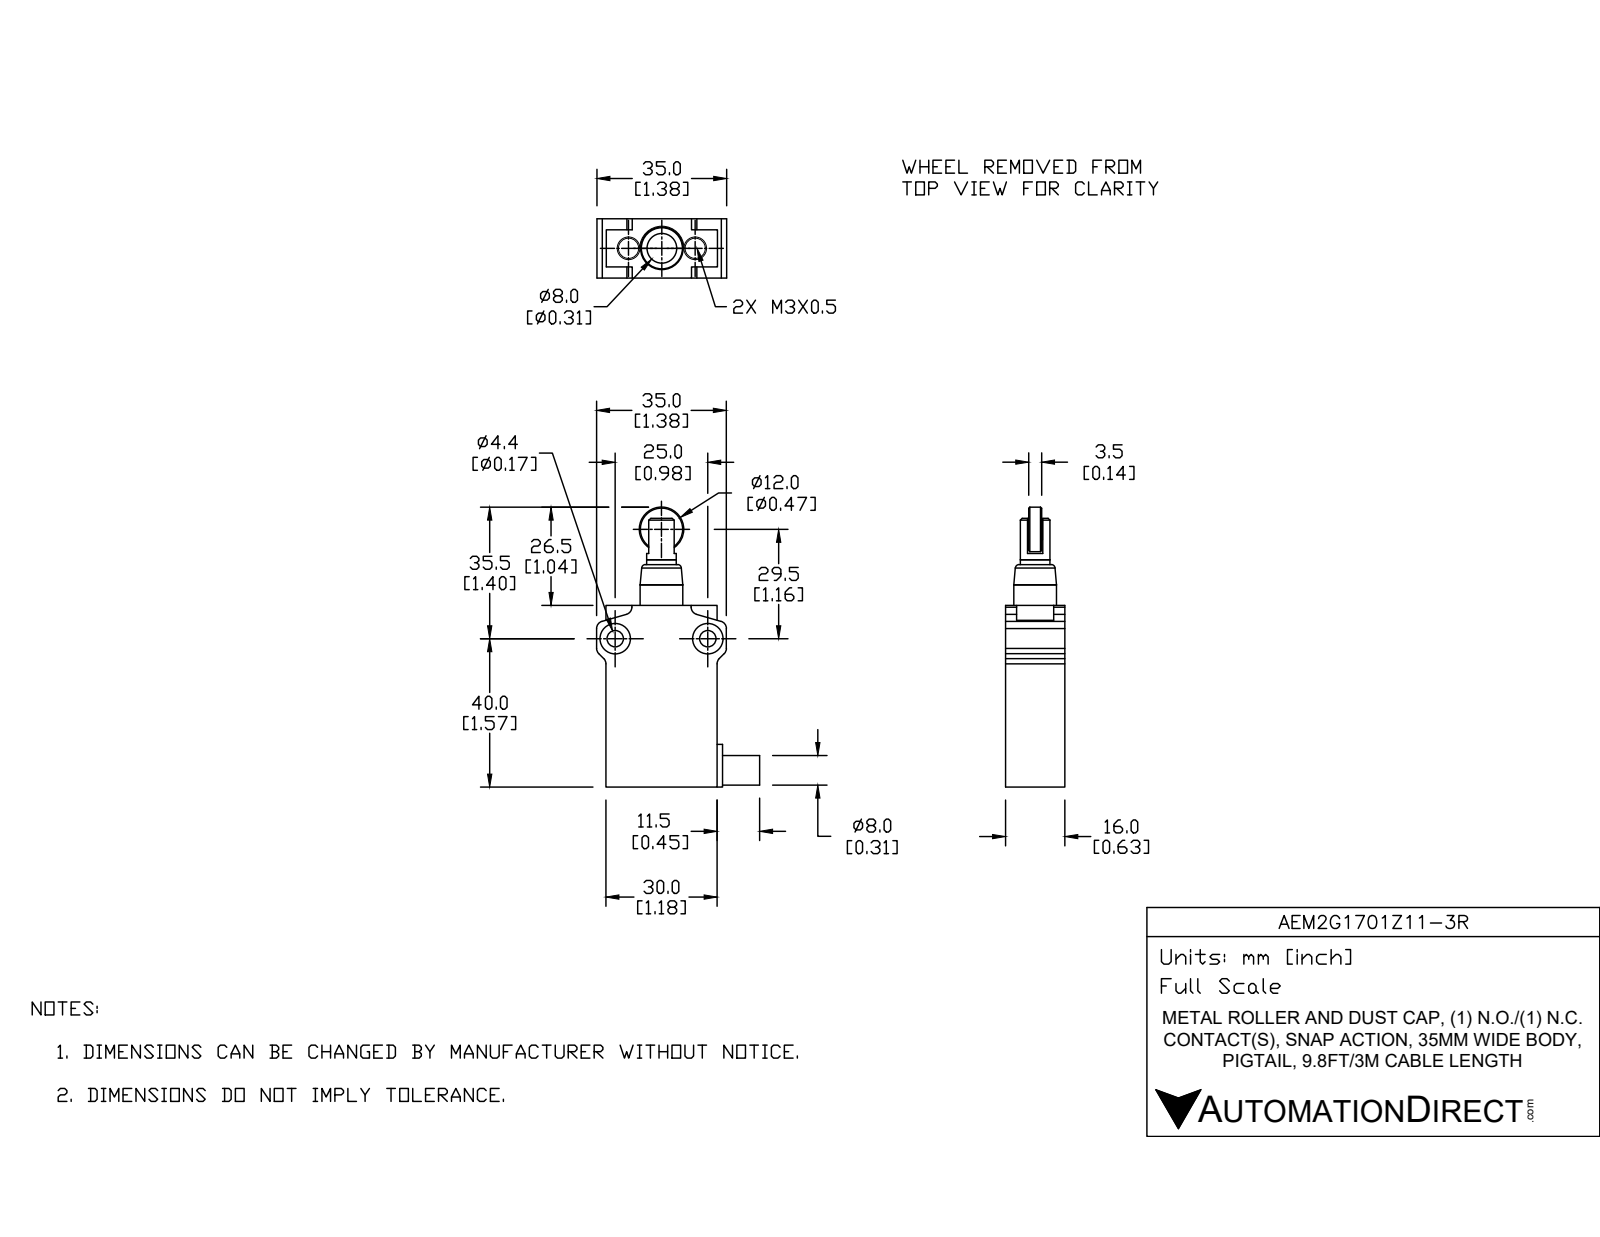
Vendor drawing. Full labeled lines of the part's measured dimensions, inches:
Part name (STEP PRODUCT): AEM2G1701Z11-3R
STEP written by: SolidWorks 2017 (AUTOMOTIVE_DESIGN)
Units: inches
Bodies: 6 solids, 129 faces (56 planar, 54 cylindrical, 19 other)
Overall size (bounding box): 2.972 × 1.87 × 0.63
Volume: 1.589 in³ · Surface area: 13.92 in²
Round holes (diameter × count): ⌀0.118 ×2, ⌀0.173 ×2, ⌀0.323 ×2
Round bosses / shafts (diameter × count): ⌀0.472 ×1, ⌀0.453 ×1, ⌀0.323 ×1, ⌀0.315 ×1, ⌀0.236 ×1, ⌀0.22 ×1
Partial cylindrical surfaces — rounded edges, fillets, slot ends (radius × count): R0.079 ×8, R0.256 ×1
Main face-to-face distances: 0.63, 1.181, 1.929, 0.472, 1.74, 0.189, 0.157, 0.234, 0.238, 0.098
Hole centre spacings: 0.748, 0.984
